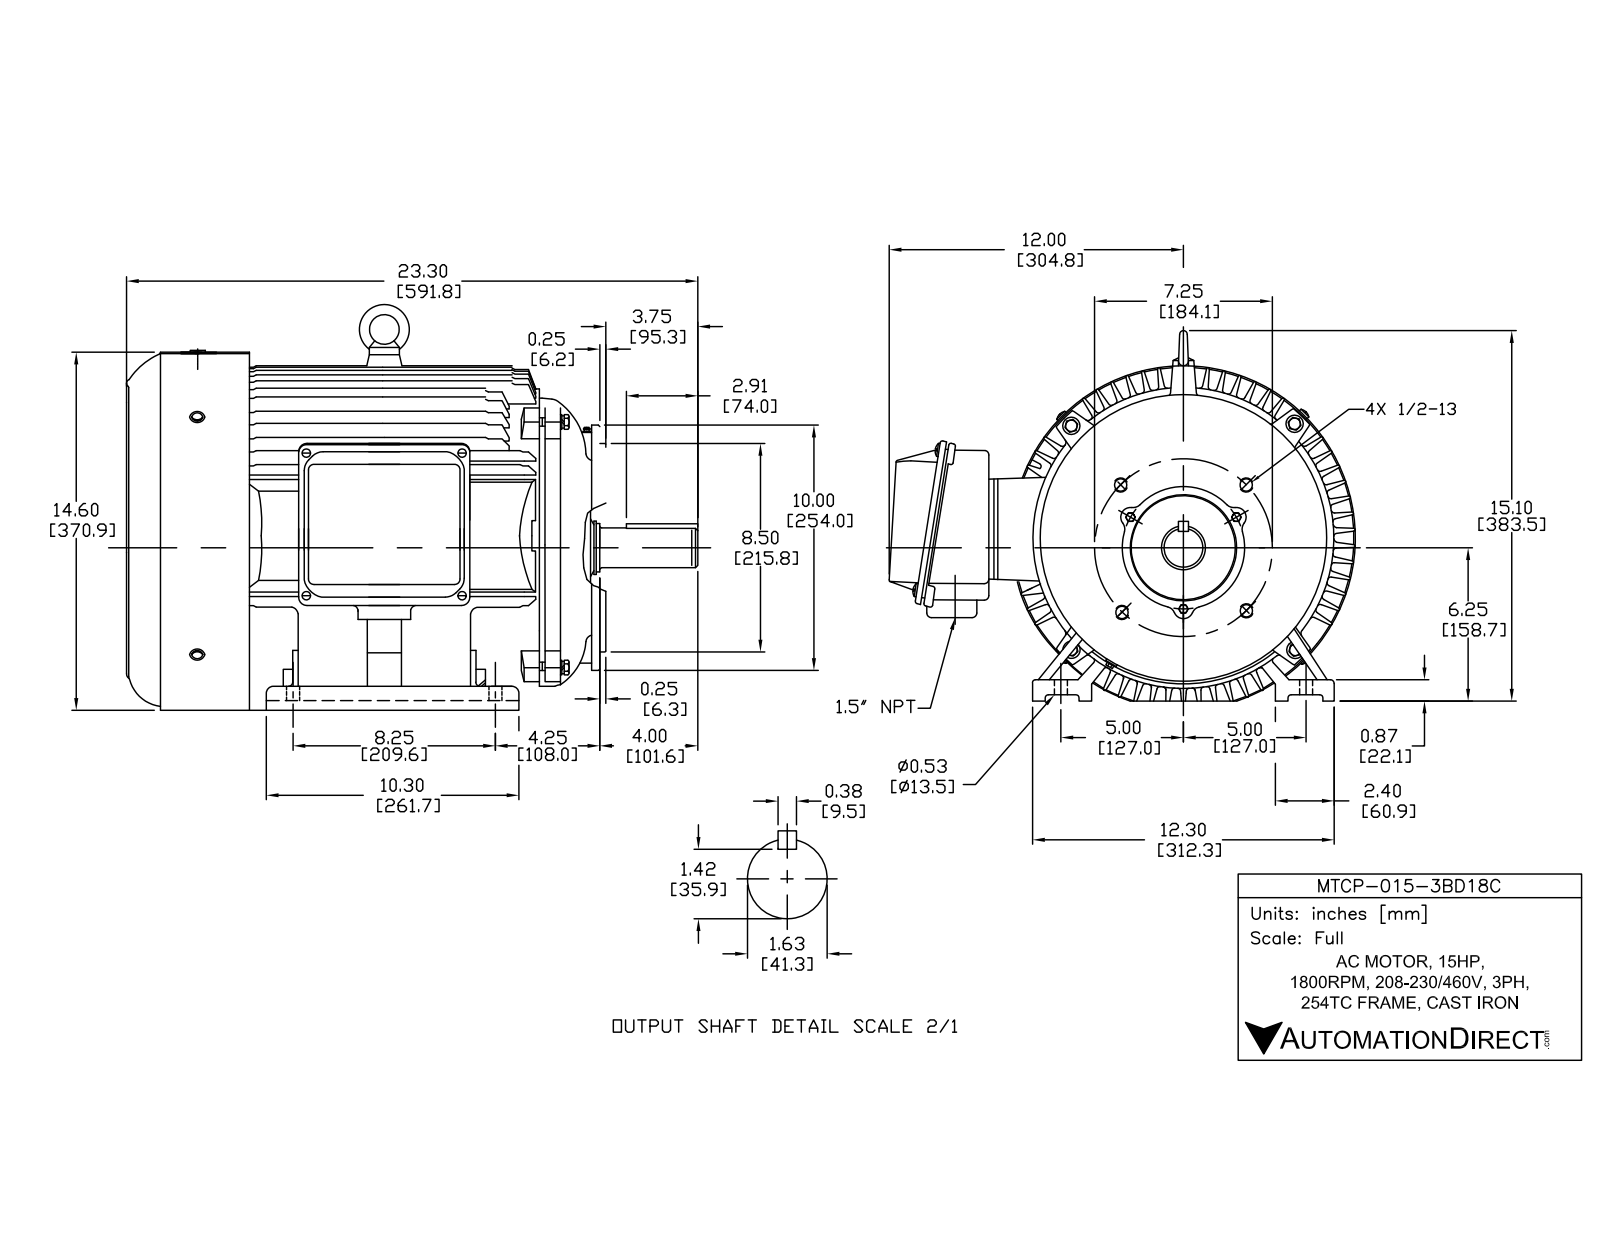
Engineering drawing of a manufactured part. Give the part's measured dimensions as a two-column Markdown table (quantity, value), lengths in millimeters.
| quantity | value |
| --- | --- |
| part name | plain washers-chamfered--normal series-a gb_GB_FASTENER_WASHER_SWCA 10; 17橡皮塞; MTCP254TC; hex head bolts-full thread grade c gb_GB_FASTENER_BOLT_HHBFTC M10X45-N (+8 more) |
| STEP written by | SolidWorks 2017 (AUTOMOTIVE_DESIGN) |
| units | millimeters |
| bodies | 67 solids, 3444 faces (903 planar, 1289 cylindrical, 1252 other) |
| overall size | 598.9 × 469.92 × 397.85 |
| volume | 9 051 000 mm³ |
| surface area | 2 376 000 mm² |
| round holes (diameter × count) | 7 × 14, 5 × 12, 8 × 8, 10.72 × 8, 17 × 5, 6.4 × 4, 6.68 × 4, 8.5 × 4, 9 × 4, 10.5 × 4, 10.9 × 4, 11 × 4 |
| round bosses / shafts (diameter × count) | 6 × 11, 12 × 5, 10 × 5, 20 × 4, 16.1 × 4, 9.88 × 4, 5 × 2, 355 × 1 |
| partial cylindrical surfaces (radius × count) | 1 × 205, 0.5 × 92, 5 × 80, 3 × 72, 4 × 38, 1.5 × 36, 8 × 26, 10 × 20 |
| main face-to-face distances | 5, 1.5, 33, 17, 469.8, 468.3, 10, 77.94, 23, 18.25 |
| hole center spacings | 75, 57.5, 70.47, 116.73, 186.34, 74.99, 92.08, 106.06 |
